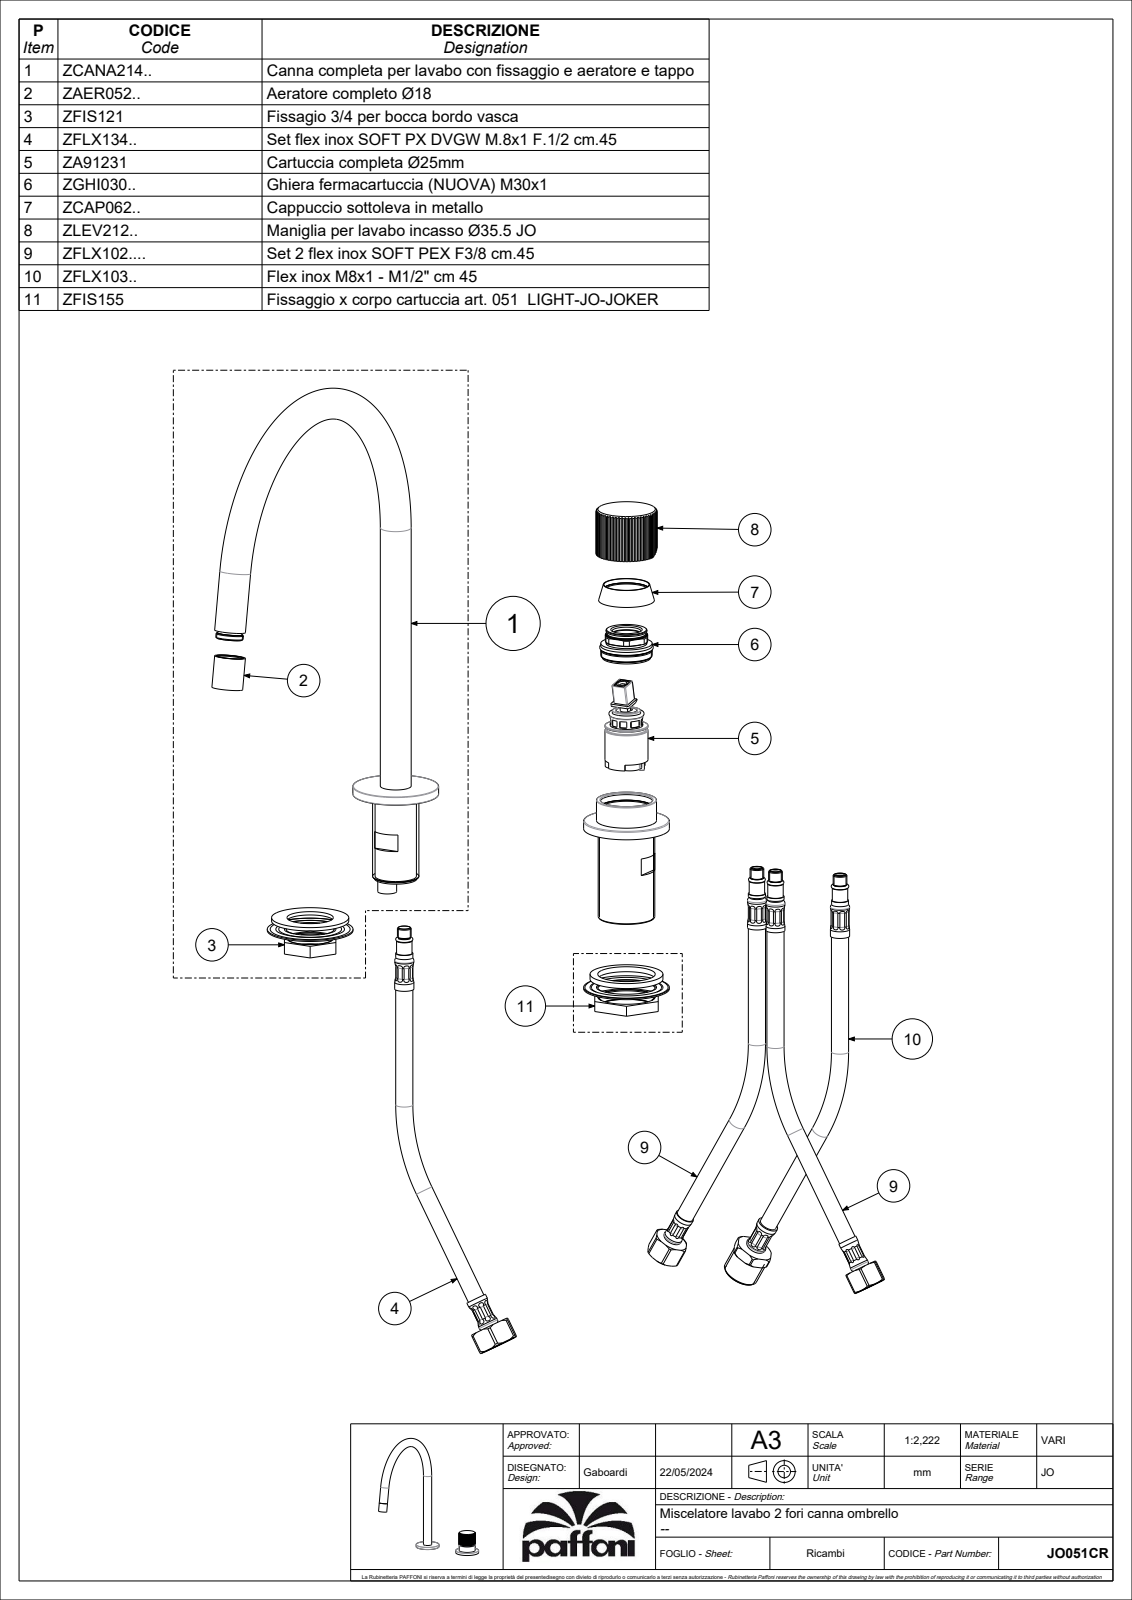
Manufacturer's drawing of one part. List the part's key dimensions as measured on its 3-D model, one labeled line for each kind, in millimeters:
Part name (STEP PRODUCT): JO051CR
STEP written by: CREO PARAMETRIC BY PTC INC, 2023092 (CONFIG_CONTROL_DESIGN)
Units: millimetres
Bodies: 2 solids, 298 faces (182 planar, 91 cylindrical, 25 other)
Overall size (bounding box): 264.31 × 230.29 × 150
Volume: 176 925 mm³ · Surface area: 45 876 mm²
Round holes (diameter × count): ⌀8 ×1, ⌀33.3 ×1
Round bosses / shafts (diameter × count): ⌀50 ×2, ⌀18 ×2, ⌀35 ×1, ⌀6.2 ×1
Partial cylindrical surfaces — rounded edges, fillets, slot ends (radius × count): R0.5 ×2, R1 ×2, R3 ×1, R4.9 ×1, R5.5 ×1, R11.5 ×1, R17.75 ×1
Main face-to-face distances: 5, 33.35, 28.35, 27, 22, 6.35, 9.5, 17.5, 12.5, 15.85
